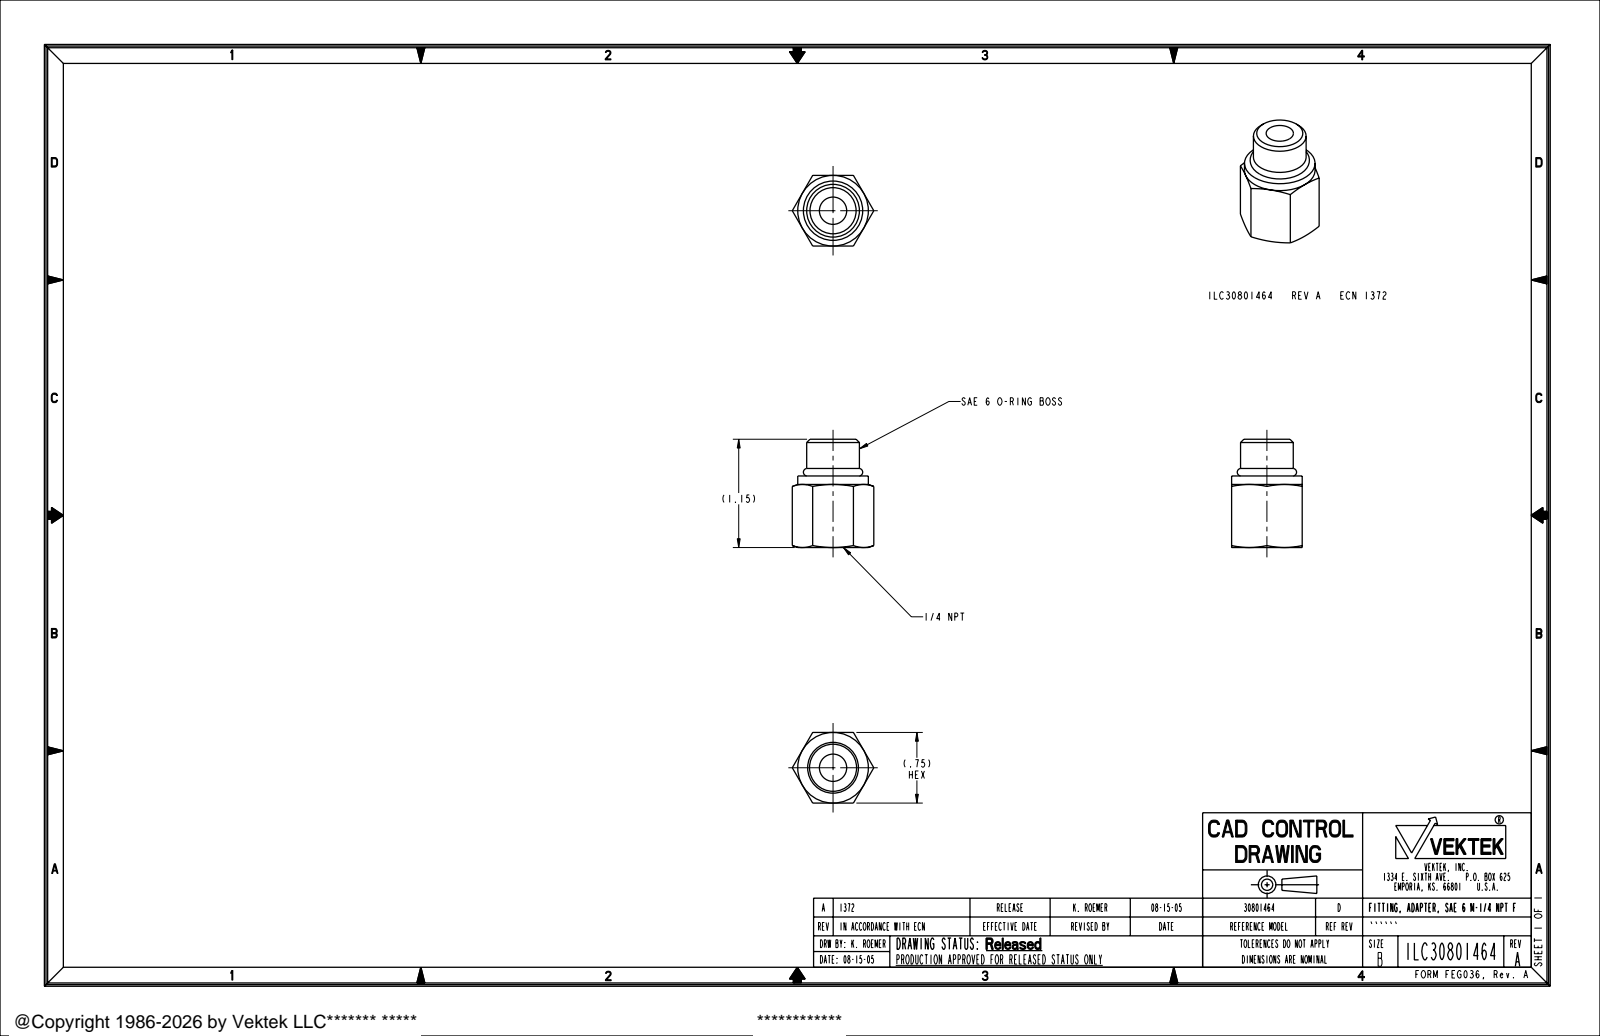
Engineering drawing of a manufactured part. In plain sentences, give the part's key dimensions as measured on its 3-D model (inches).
The part is named "ILC30801464". Its 3-D file was written by "PRO/ENGINEER BY PARAMETRIC TECHNOLOGY CORPORATION, 2004290 (AUTOMOTIVE_DESIGN_CC2)". It is 1 solid with 39 faces: 10 planar, 10 cylindrical and 19 other. Overall it measures 1.15 by 0.866 by 0.75 inches. Its volume is 0.301 cubic inches and its surface area 4.952 square inches. Round holes: 1 of diameter 0.29, 1 of diameter 0.5. Round bosses or shafts: 1 of diameter 0.75, 1 of diameter 0.56. The main face-to-face distances are 0.75, 0.76, 0.66, 0.1, 1.15, 0.49, 0.39.
